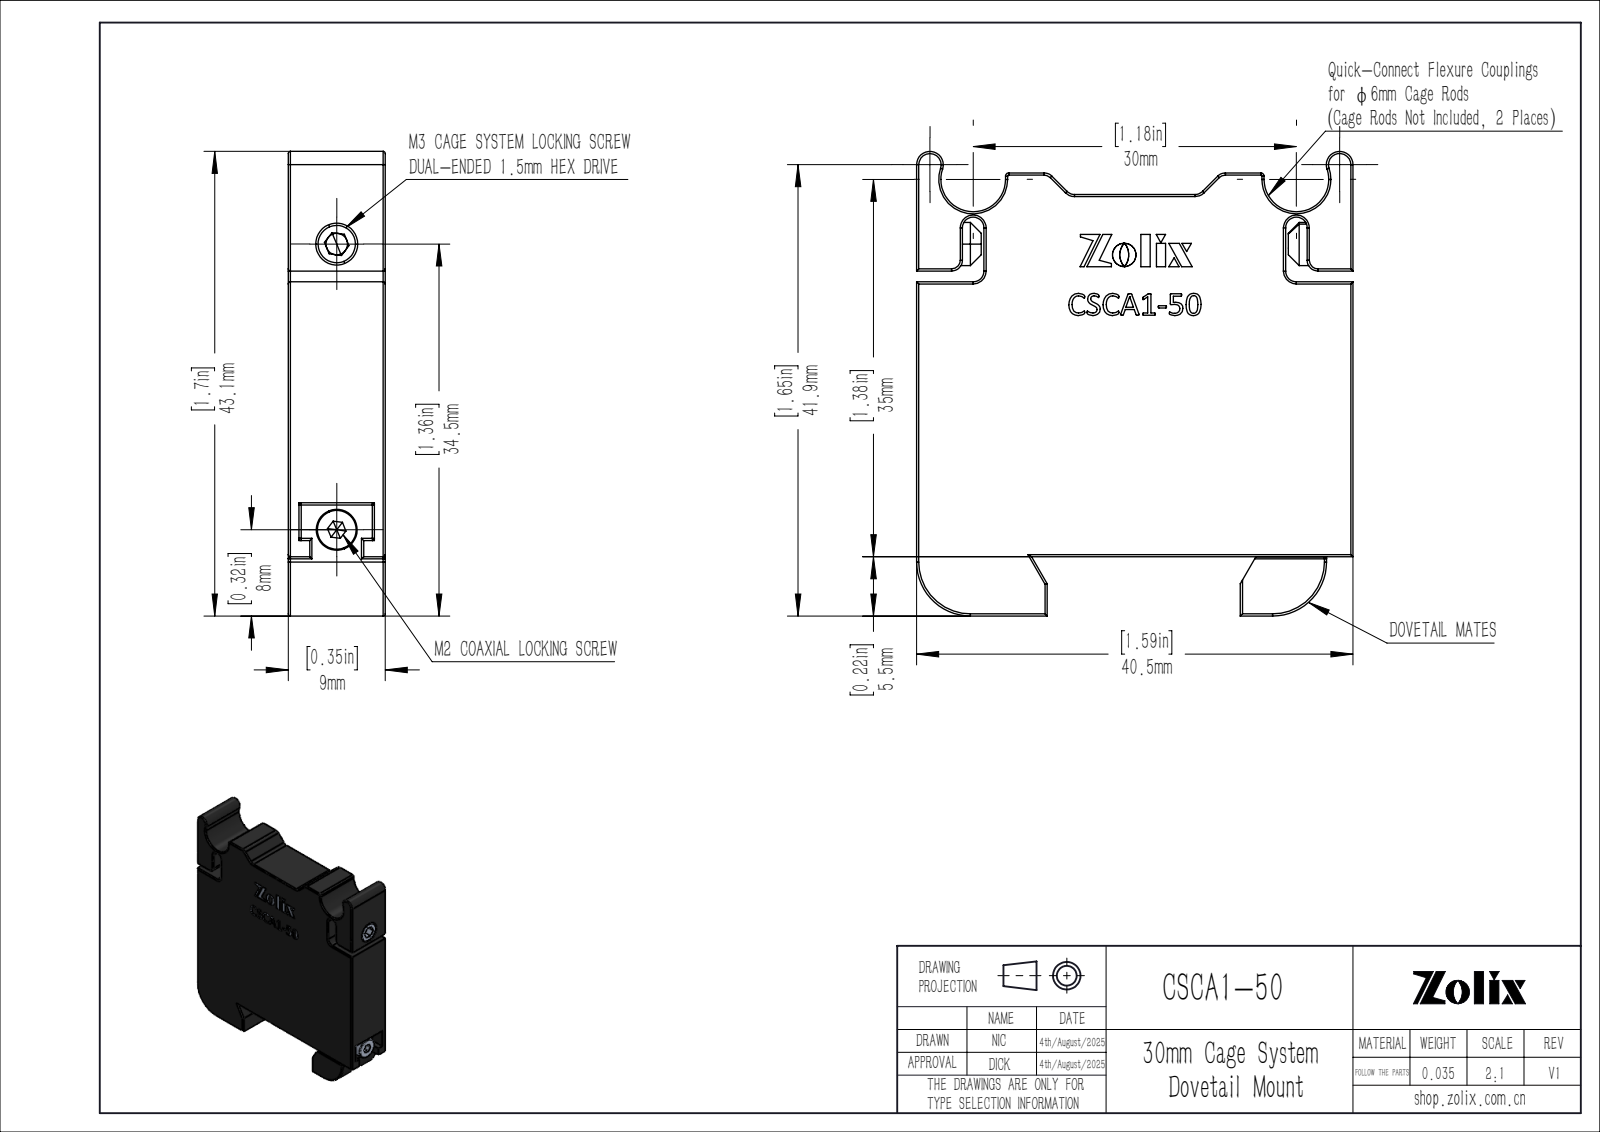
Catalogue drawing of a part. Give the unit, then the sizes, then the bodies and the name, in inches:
Units: inches
Overall size (bounding box): 1.697 × 1.594 × 0.354
Round holes (diameter × count): ⌀0.063 ×1, ⌀0.098 ×1, ⌀0.13 ×1
Round bosses / shafts (diameter × count): ⌀0.157 ×1, ⌀0.15 ×1, ⌀0.079 ×1
Partial cylindrical surfaces — rounded edges, fillets, slot ends (radius × count): R0.008 ×60, R0.039 ×10, R0.012 ×2, R0.049 ×2, R0.079 ×2, R0.118 ×2, R0.197 ×1, R0.197 ×1
Main face-to-face distances: 0.354, 1.594, 0.039, 0.197, 0.079, 0.276, 0.315, 1.323, 1.126, 1.004
Hole centre spacings: 1.043
Volume: 0.787 in³ · Surface area: 9.04 in²
Bodies: 5 solids, 564 faces (297 planar, 114 cylindrical, 153 other)
Part name (STEP PRODUCT): CSCA1-50
STEP written by: SolidWorks 2020 (CONFIG_CONTROL_DESIGN)
